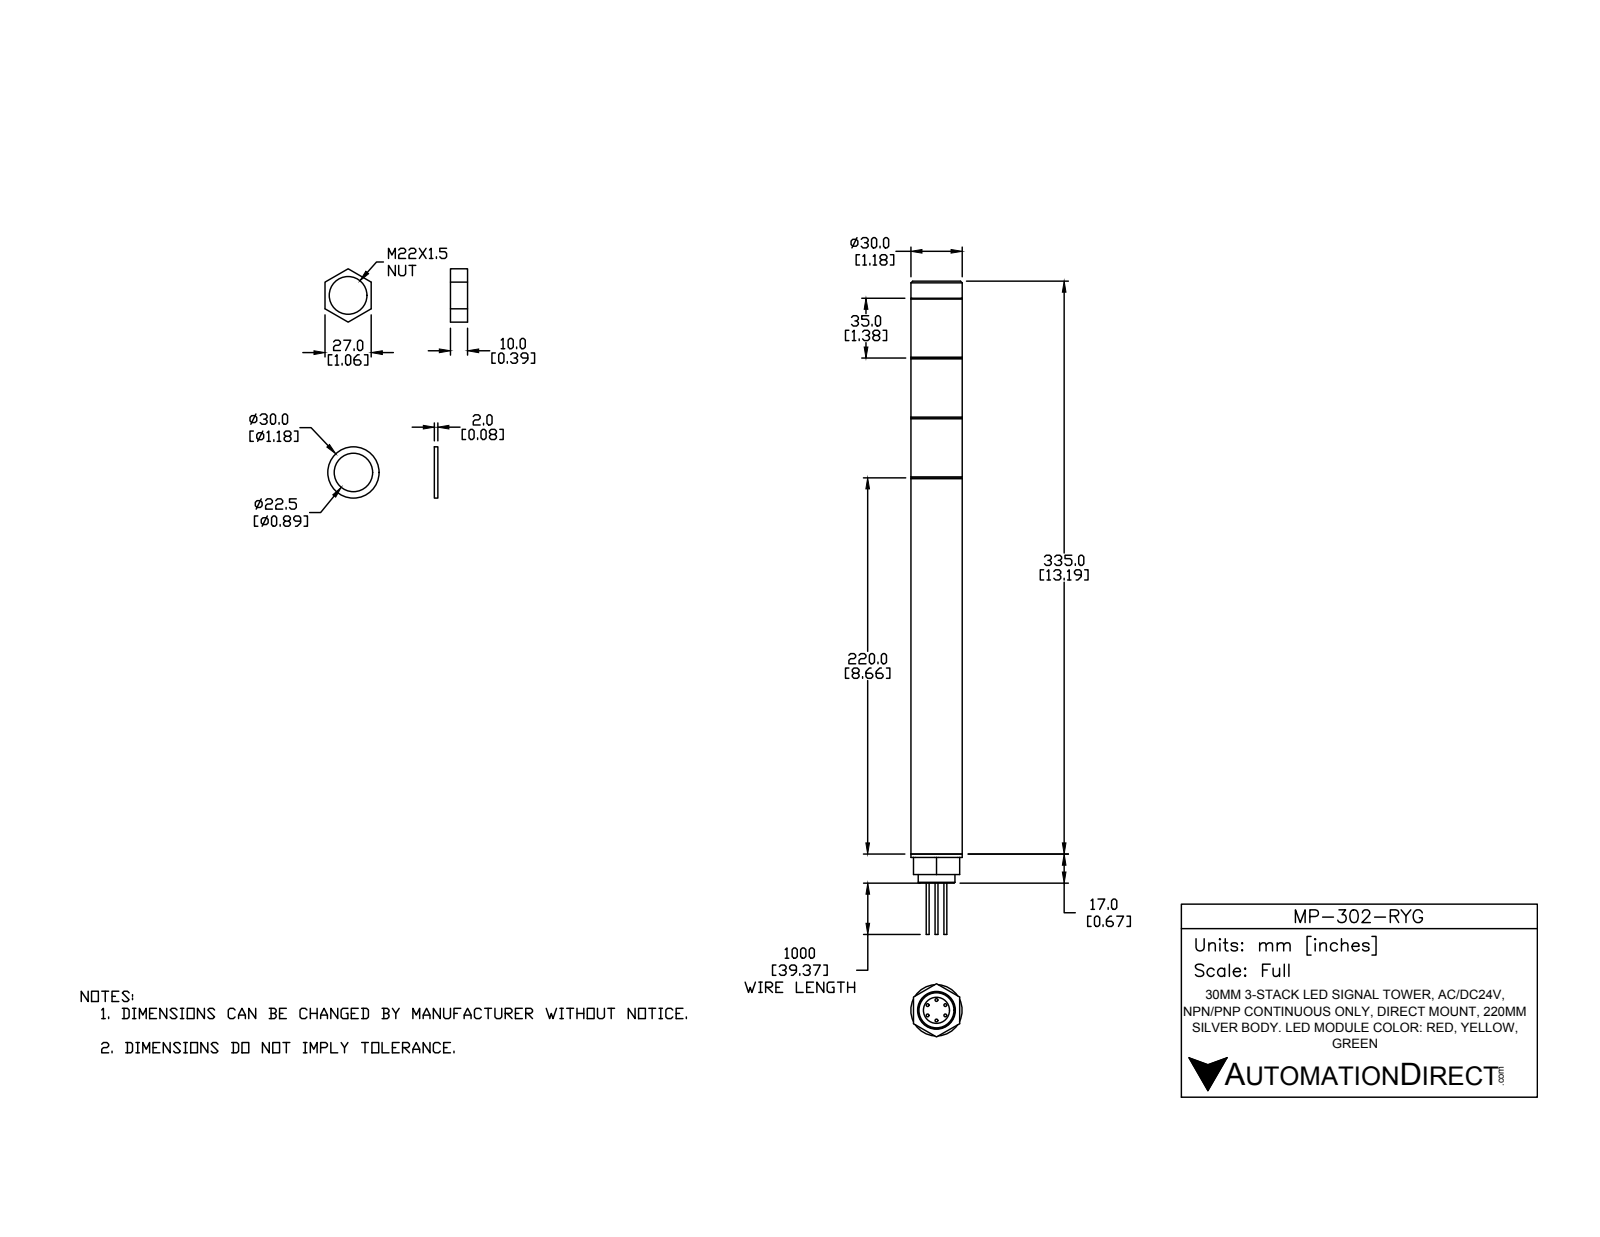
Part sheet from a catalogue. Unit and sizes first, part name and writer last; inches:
Units: inches
Overall size (bounding box): 15.039 × 1.228 × 1.181
Round holes (diameter × count): ⌀0.126 ×1, ⌀0.303 ×1, ⌀0.602 ×1, ⌀0.815 ×1, ⌀0.866 ×1
Round bosses / shafts (diameter × count): ⌀0.067 ×6, ⌀1.181 ×1, ⌀0.846 ×1, ⌀0.197 ×1
Main face-to-face distances: 1.378, 2.756, 4.134, 8.74, 10.118, 11.496, 1.772, 13.268, 8.661, 10.039
Volume: 14.2 in³ · Surface area: 75.53 in²
Bodies: 14 solids, 111 faces (51 planar, 40 cylindrical, 20 other)
Part name (STEP PRODUCT): MP-302-RYG
STEP written by: SolidWorks 2016 (AUTOMOTIVE_DESIGN)
